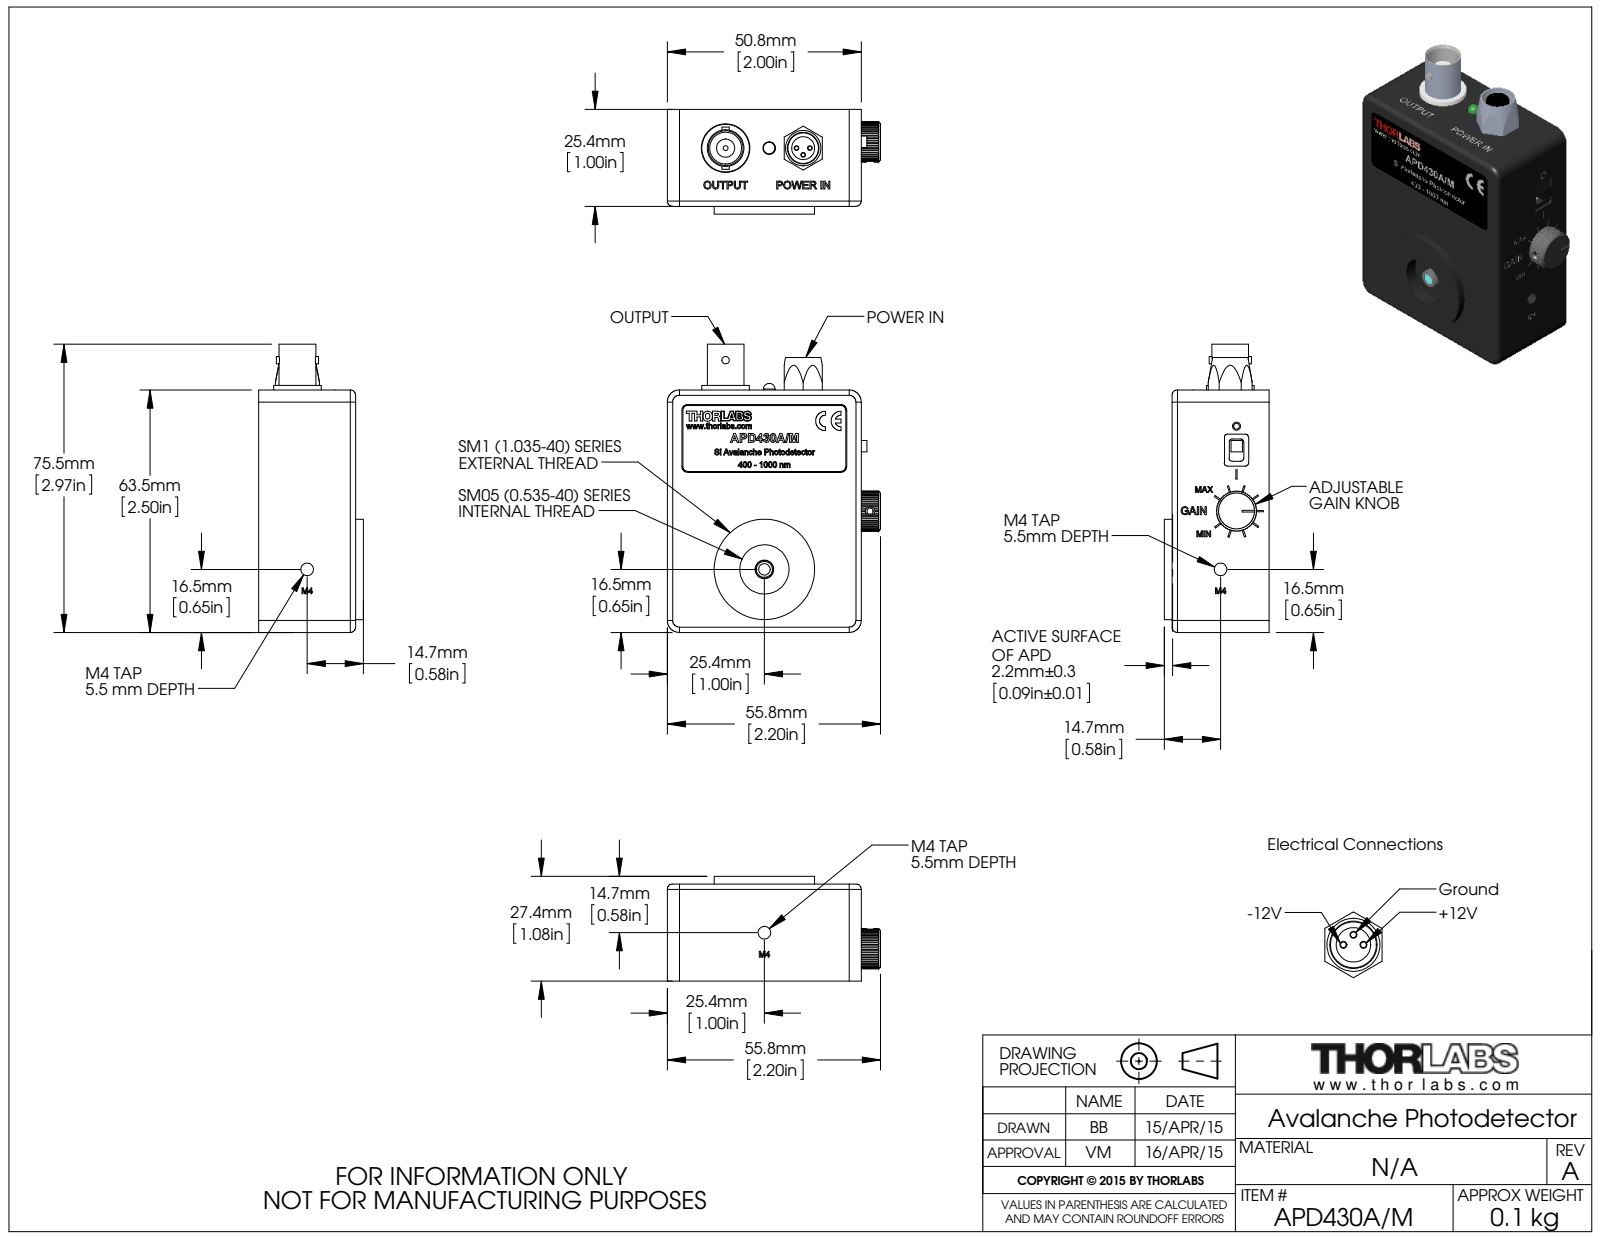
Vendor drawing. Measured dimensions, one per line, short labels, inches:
name: MTN004938
written by: SolidWorks 2014 (AUTOMOTIVE_DESIGN)
unit: in
bodies: 0 solids, 2321 faces (1266 planar, 436 cylindrical, 619 other)
size: 2.971 × 2.197 × 1.08
holes: 9× ⌀0.063, 6× ⌀0.02, 4× ⌀0.094, 2× ⌀0.018, 2× ⌀0.098, 2× ⌀0.13, 1× ⌀0.05, 1× ⌀0.052, 1× ⌀0.083, 1× ⌀0.118, 1× ⌀0.13, 1× ⌀0.138
bosses: 5× ⌀0.039, 4× ⌀0.15, 4× ⌀0.079, 2× ⌀0.065, 2× ⌀0.063, 2× ⌀0.051, 1× ⌀1.035, 1× ⌀0.49
rounds: 53× R0.012, 19× R0.125, 14× R0.13, 8× R0.031, 8× R0.095, 6× R0.02, 6× R0.075, 5× R0.008
face distances: 0.063, 0.1, 0.016, 0.872, 0.935, 1, 0.937, 0.065, 0.984, 0.922
hole spacings: 1.621, 0.174, 2.013, 2.579, 0.098, 1.711, 0.05, 0.079
